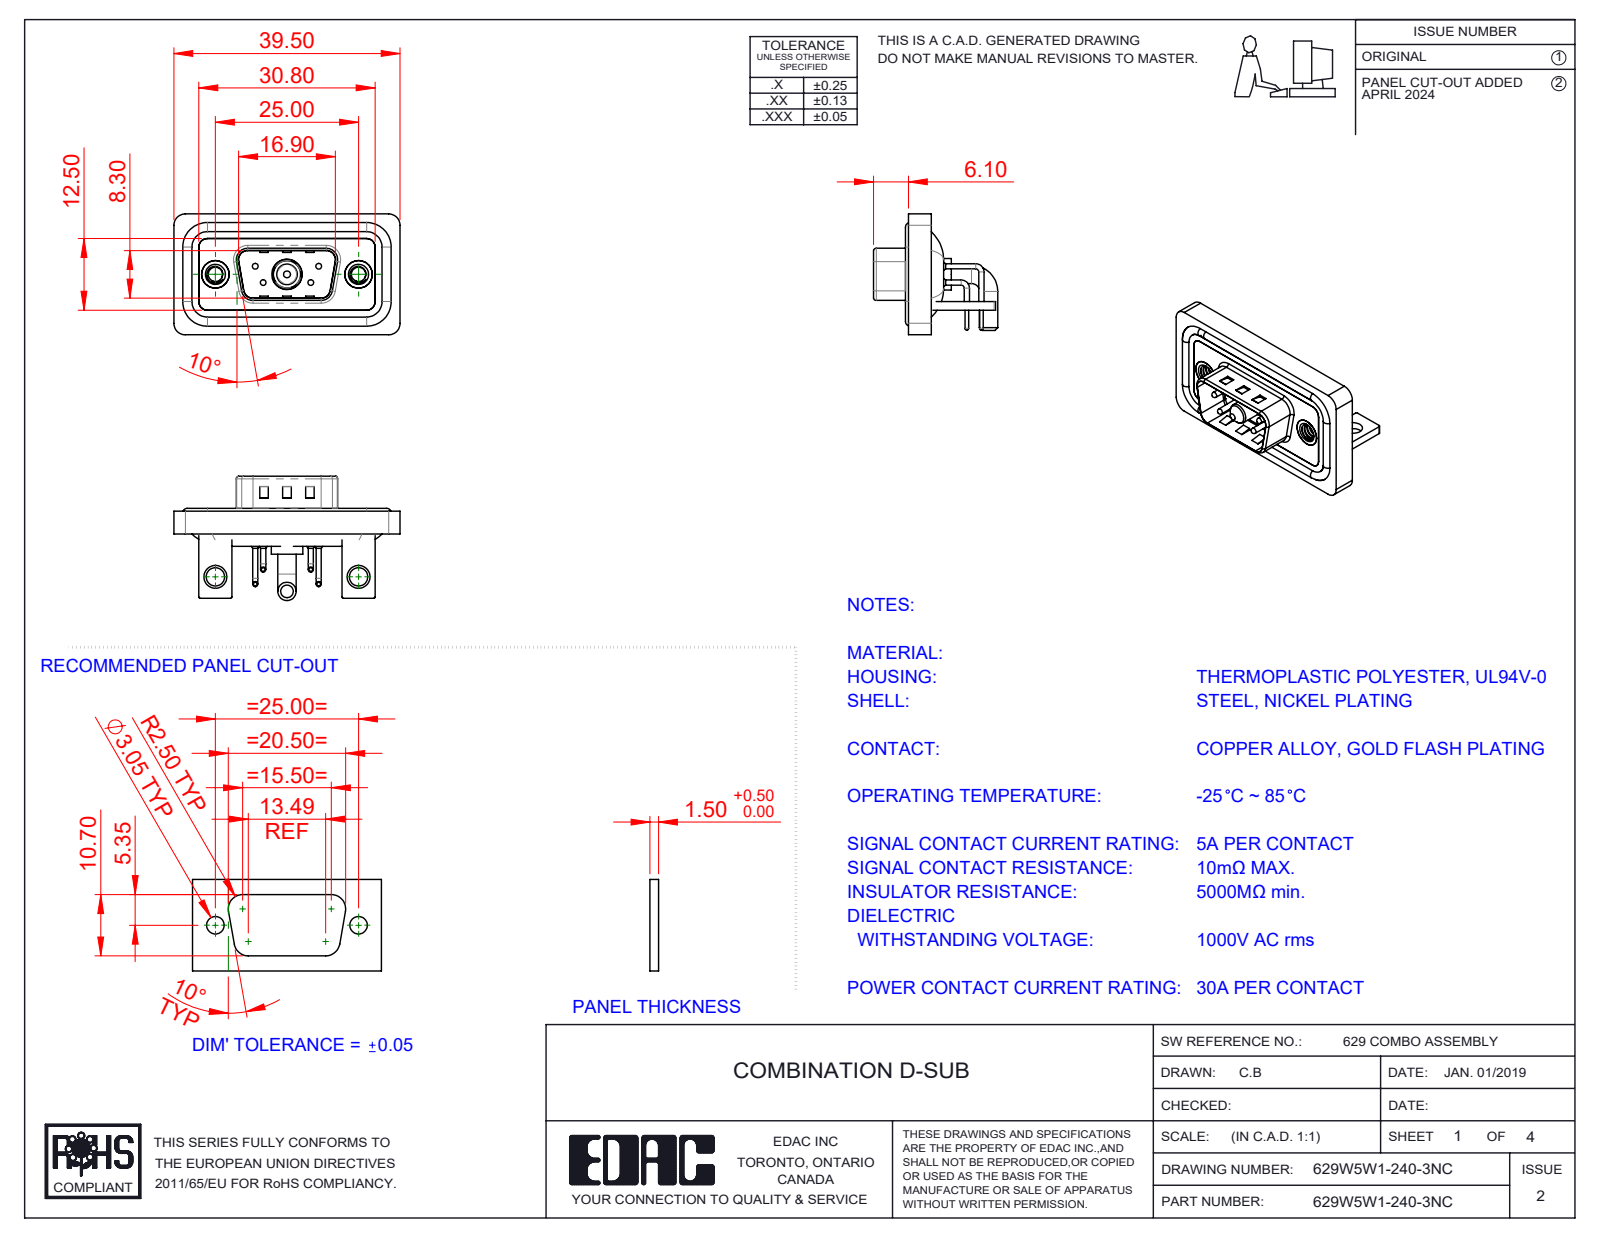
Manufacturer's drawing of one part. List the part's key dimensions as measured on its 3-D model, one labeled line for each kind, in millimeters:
Part name (STEP PRODUCT): 629Combo Stabilizer Bracket; 629W5W1-140-3NC; 629Combo Waterproof Housing_09 Contacts; 629Combo Housing_5W1 (+6 more)
STEP written by: SolidWorks 2023 (CONFIG_CONTROL_DESIGN)
Units: millimetres
Bodies: 15 solids, 932 faces (431 planar, 363 cylindrical, 138 other)
Overall size (bounding box): 39.5 × 21.7 × 21.1
Volume: 4 776 mm³ · Surface area: 7 770 mm²
Round holes (diameter × count): ⌀0.75 ×4, ⌀1.6 ×4, ⌀2 ×4, ⌀2.5 ×2, ⌀3.2 ×2, ⌀4 ×2, ⌀4.8 ×2, ⌀5 ×2, ⌀4.85 ×1, ⌀5.3 ×1
Round bosses / shafts (diameter × count): ⌀0.9 ×8, ⌀1.6 ×4, ⌀1.5 ×4, ⌀1 ×4, ⌀0.65 ×4, ⌀4.9 ×2, ⌀3.2 ×2, ⌀5.5 ×1
Partial cylindrical surfaces — rounded edges, fillets, slot ends (radius × count): R2 ×19, R1.5 ×18, R0.25 ×16, R0.5 ×9, R1.6 ×8, R0.6 ×4, R0.65 ×4, R0.9 ×4
Main face-to-face distances: 0.4, 1.5, 0.8, 2.9, 1.1, 2.1, 1.2, 1.6, 2.5, 3.7
Hole centre spacings: 3.16, 5.72, 7.1, 12.5, 18.1, 25, 4.39, 4.4
